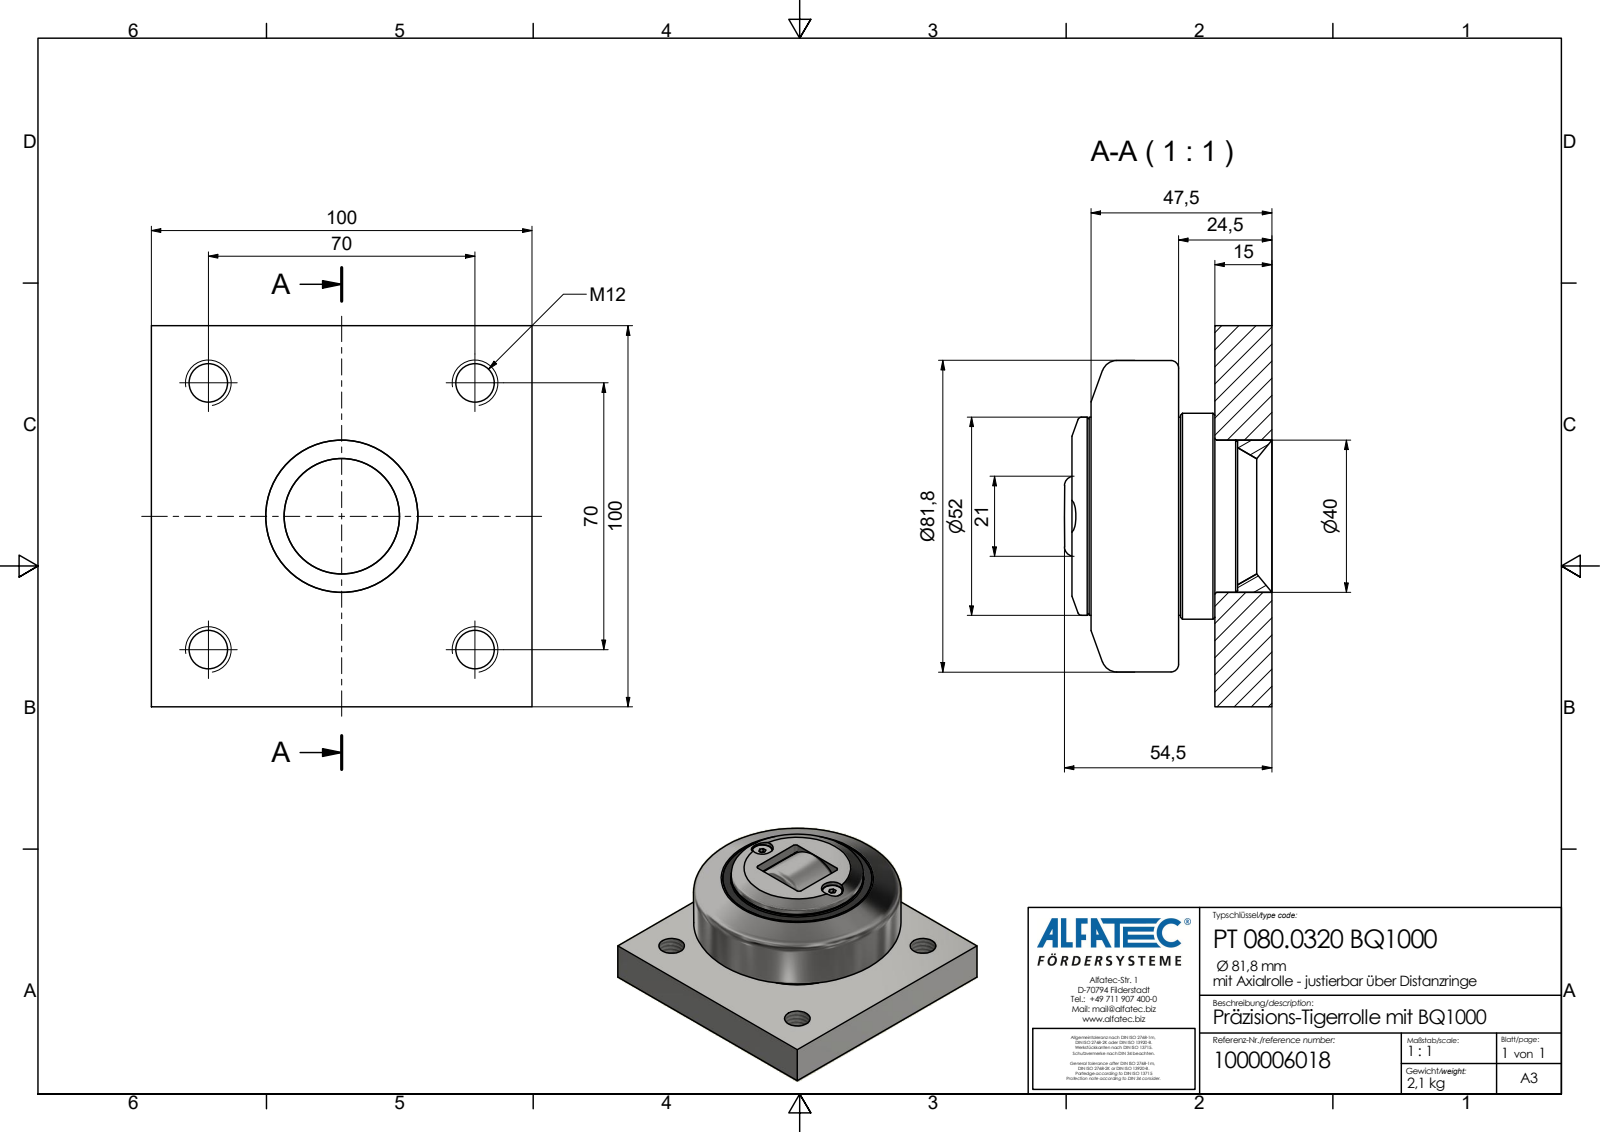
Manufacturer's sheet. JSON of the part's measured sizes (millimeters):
{"part_name": "PT 080.0320 BQ1000_Kontur", "step_written_by": "Autodesk Inventor 2020 (AP242_MANAGED_MODEL_BASED_3D_ENGINEERING_MIM_LF)", "units": "millimeters", "bodies": {"solids": 1, "faces": 98, "planar": 46, "cylindrical": 31, "other": 21}, "overall_size": [100, 100, 54.5], "volume_mm3": 287184, "surface_area_mm2": 43461, "round_holes": [[10.11, 4], [4.5, 2], [8.6, 2], [46.2, 1]], "round_bosses_or_shafts": [[7.8, 2], [4, 2], [54, 1], [52, 1], [32.8, 1]], "partial_cylinders_radius": [[1, 4], [8, 1], [9, 1], [10.5, 1]], "face_to_face_distances": [15, 100, 24.5, 9.5, 0.5, 23.5, 47.5, 32.5, 23, 48], "hole_center_spacings": [38.28, 49.5, 64.77, 70, 19.5, 98.99, 39]}
